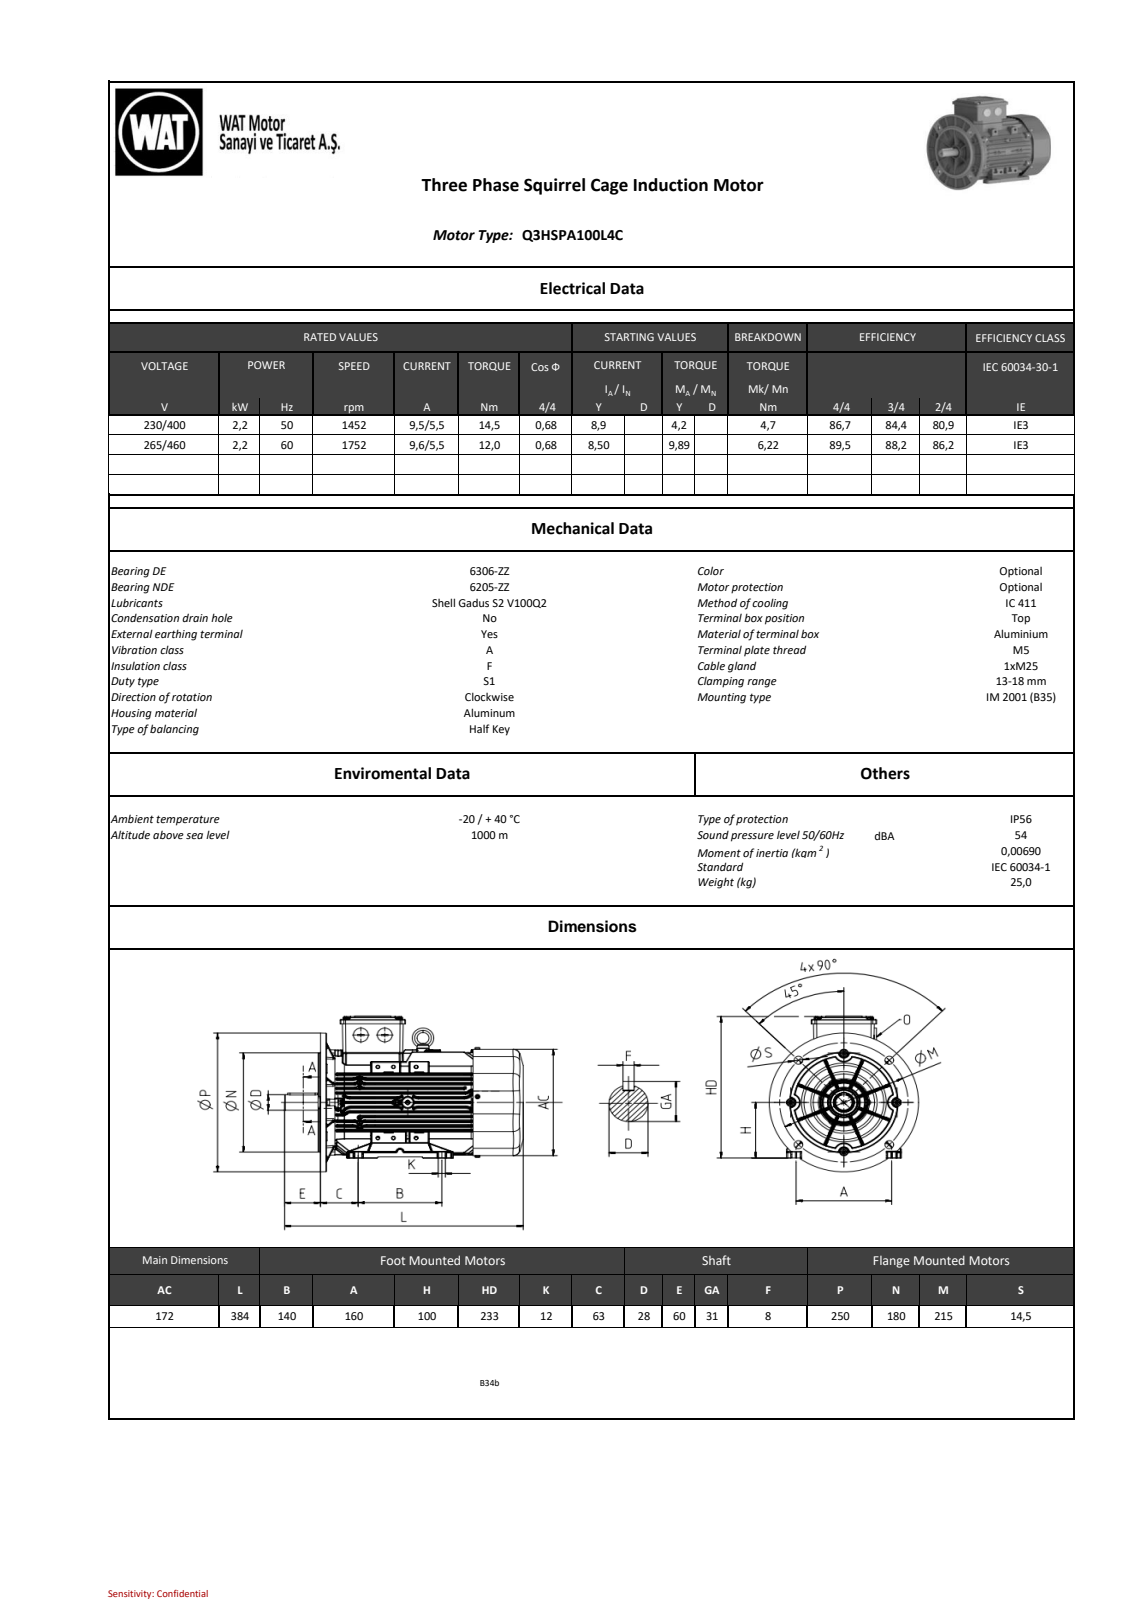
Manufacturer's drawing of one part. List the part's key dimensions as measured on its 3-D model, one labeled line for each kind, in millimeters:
Part name (STEP PRODUCT): QHS Series_ 100_B35 DEEP COVER_stp_objects
STEP written by: SIEMENS PLM Software NX2206.8101 (AUTOMOTIVE_DESIGN)
Units: millimetres
Bodies: 0 solids, 7346 faces (1871 planar, 3182 cylindrical, 2293 other)
Overall size (bounding box): 384.19 × 258.21 × 250.32
Round holes (diameter × count): ⌀11 ×4, ⌀8.5 ×1, ⌀9.87 ×1, ⌀10.5 ×1, ⌀79.79 ×1, ⌀97.79 ×1, ⌀115.78 ×1
Round bosses / shafts (diameter × count): ⌀8 ×7, ⌀5 ×6, ⌀10 ×4, ⌀9.5 ×4, ⌀25 ×2, ⌀180 ×1, ⌀102.19 ×1, ⌀84.19 ×1
Partial cylindrical surfaces — rounded edges, fillets, slot ends (radius × count): R1 ×847, R0.8 ×707, R0.5 ×442, R2 ×71, R8 ×28, R1.5 ×11, R4 ×10, R0.8 ×9
Main face-to-face distances: 4, 7.5, 222, 91.91, 16, 8.93, 82.98, 23.57, 206, 7.37
Hole centre spacings: 79.4, 112.29, 158.8, 79.25, 79.55
